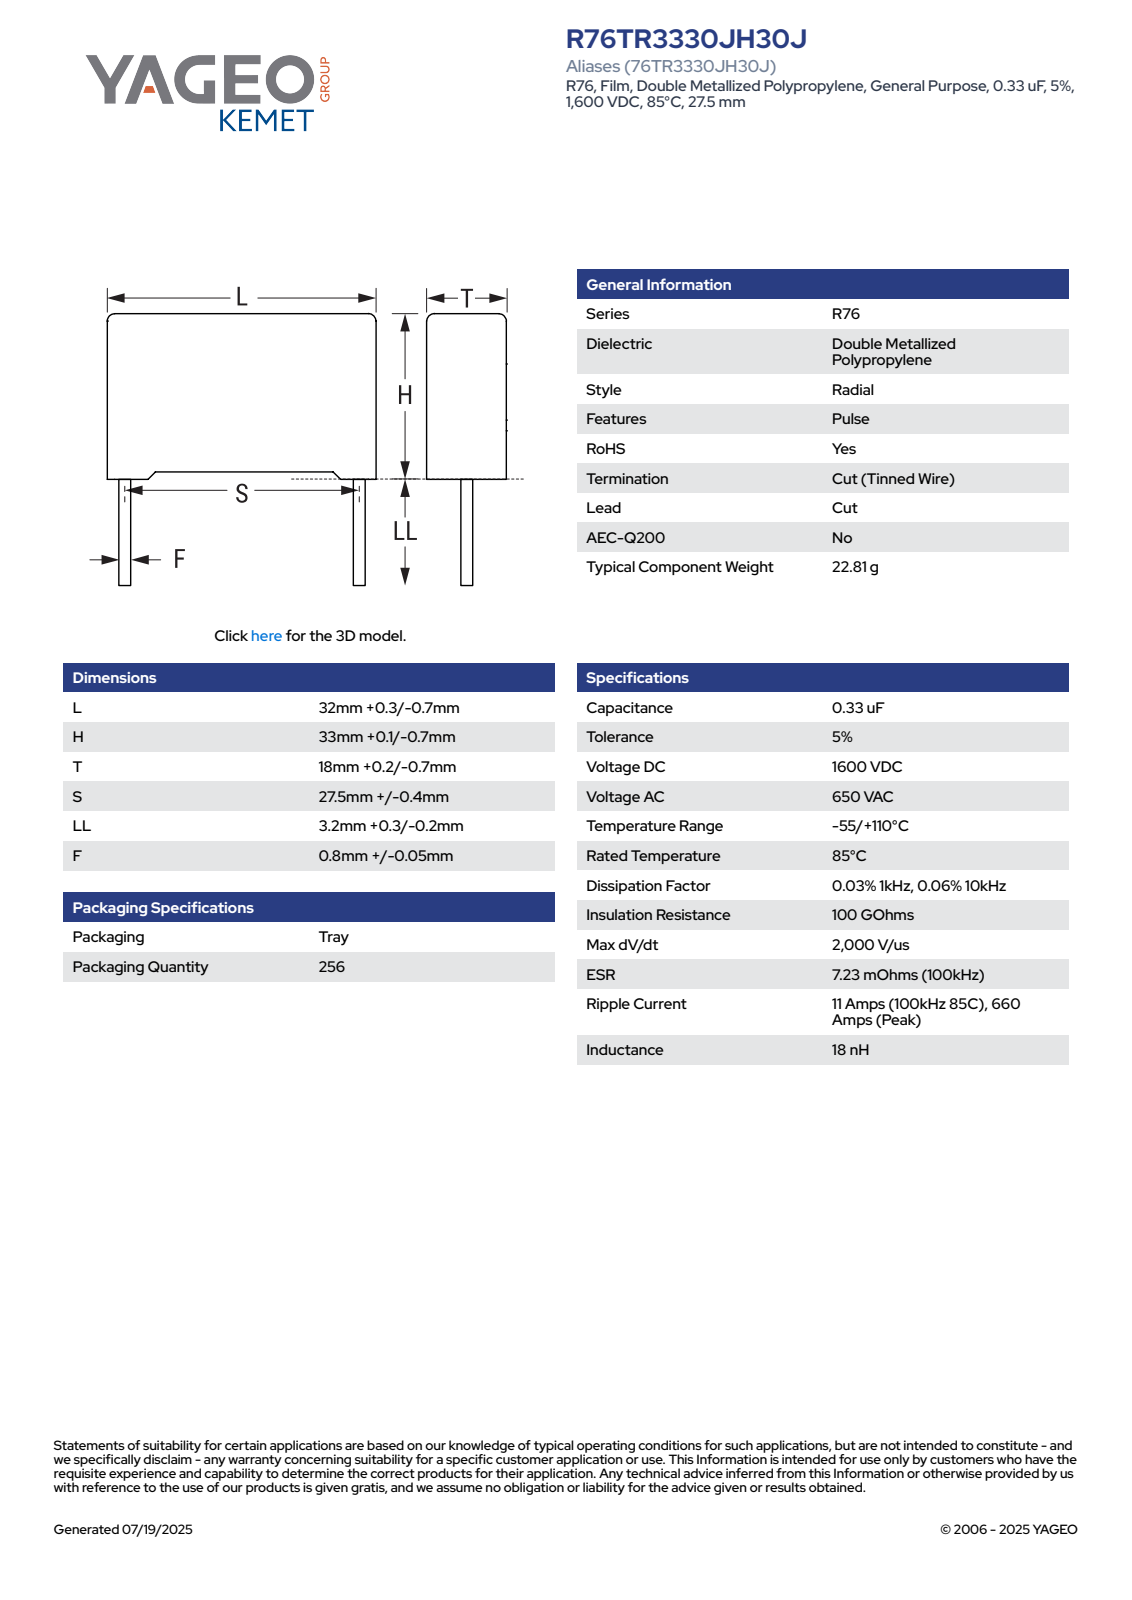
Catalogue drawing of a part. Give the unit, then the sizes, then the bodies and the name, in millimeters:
Units: millimetres
Overall size (bounding box): 36.6 × 32.3 × 18.2
Round bosses / shafts (diameter × count): ⌀0.85 ×2
Partial cylindrical surfaces — rounded edges, fillets, slot ends (radius × count): R0.5 ×4
Main face-to-face distances: 18.2, 32.3, 31.96, 0.39, 32.35, 0.75, 1.14, 33.1, 1.08, 31.22
Volume: 18 892 mm³ · Surface area: 4 586 mm²
Bodies: 4 solids, 85 faces (77 planar, 8 cylindrical, 0 other)
Part name (STEP PRODUCT): CFR_RB2_32X33X18_L32.3H33.1T18.2S27.5LL3.5F0.85
STEP written by: SolidWorks 2021 (AUTOMOTIVE_DESIGN)
